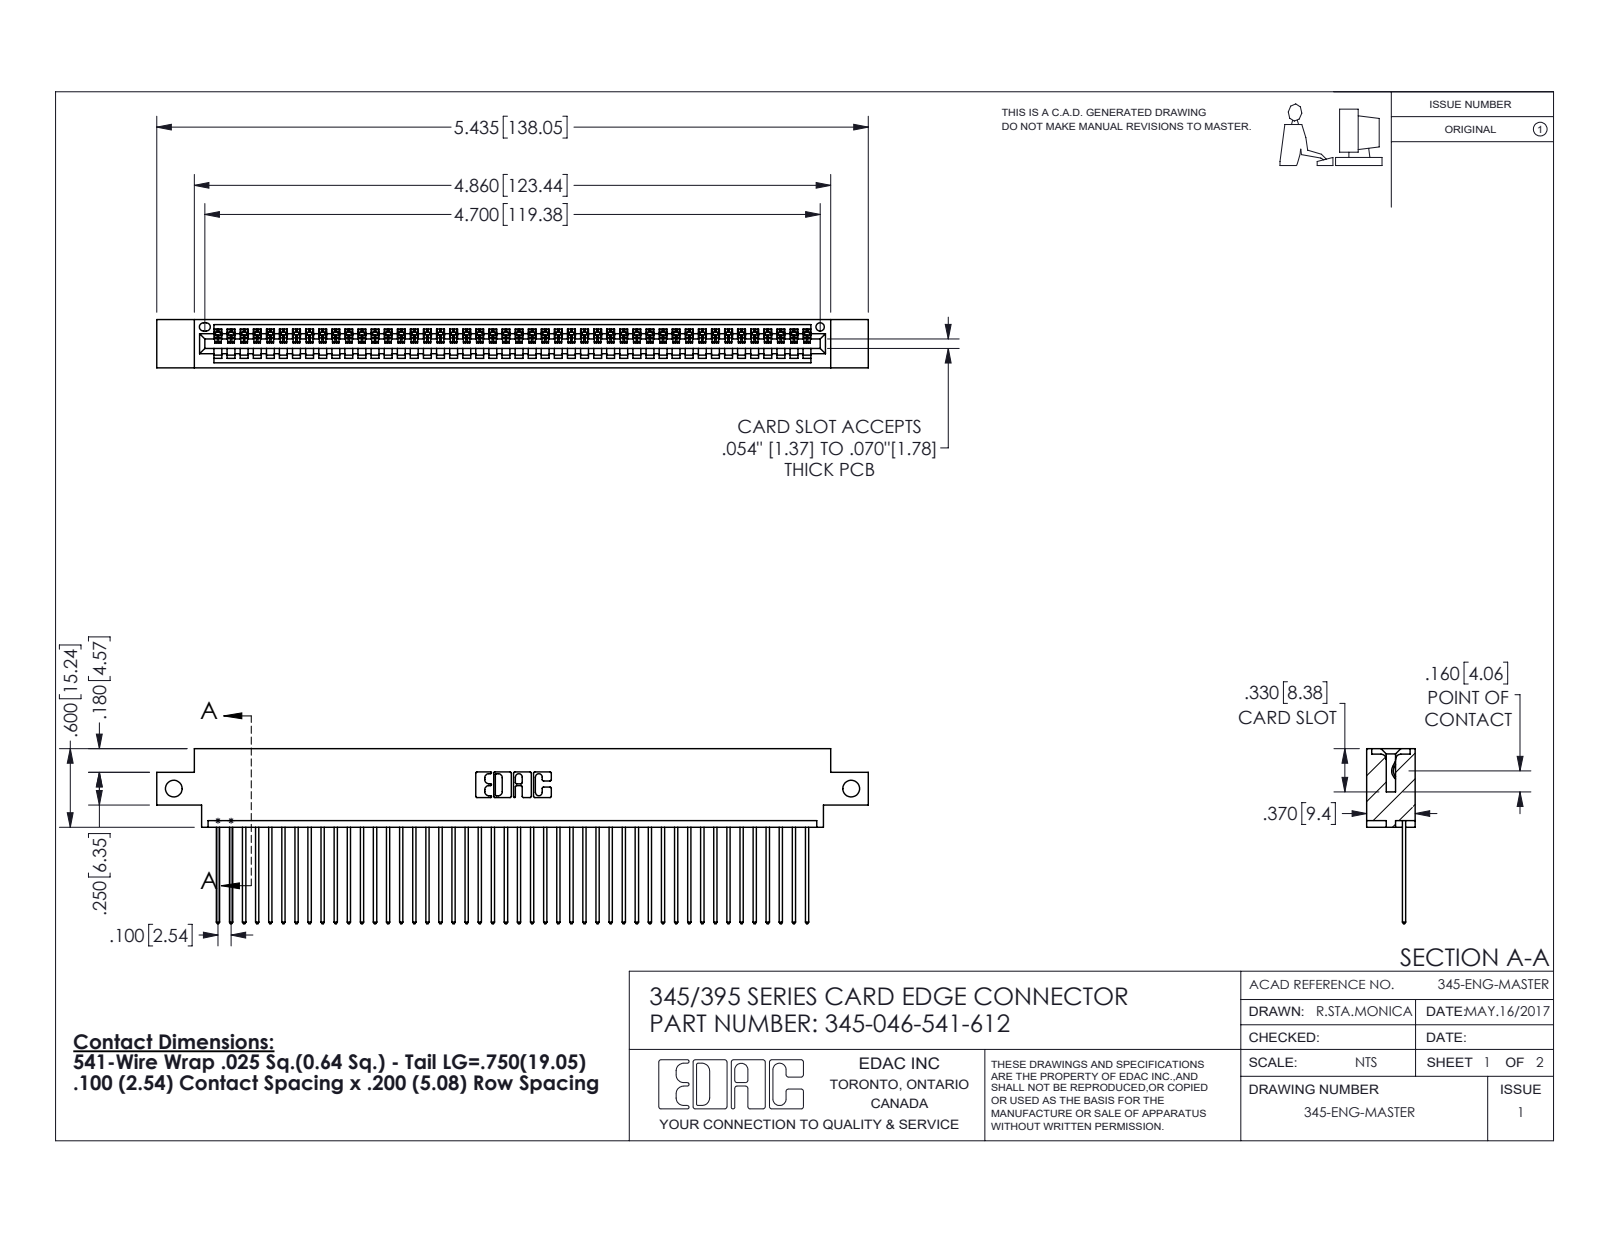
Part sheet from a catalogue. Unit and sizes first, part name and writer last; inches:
Units: inches
Overall size (bounding box): 5.435 × 1.337 × 0.37
Round holes (diameter × count): ⌀0.128 ×2, ⌀0.064 ×1
Partial cylindrical surfaces — rounded edges, fillets, slot ends (radius × count): R0.006 ×92, R0.01 ×92, R0.01 ×22, R0.007 ×6, R0.031 ×6, R0.026 ×3, R0.031 ×2, R0.04 ×2
Main face-to-face distances: 0.072, 0.298, 0.37, 0.098, 0.272, 0.025, 0.2, 0.225, 0.175, 0.149
Hole centre spacings: 5.175
Volume: 0.799 in³ · Surface area: 28.42 in²
Bodies: 47 solids, 2798 faces (1924 planar, 874 cylindrical, 0 other)
Part name (STEP PRODUCT): 345-292-001_345-293-141; 345 Part_0.170 Offset - Side Mount; 345-046-541-612
STEP written by: SolidWorks 2016 (CONFIG_CONTROL_DESIGN)
